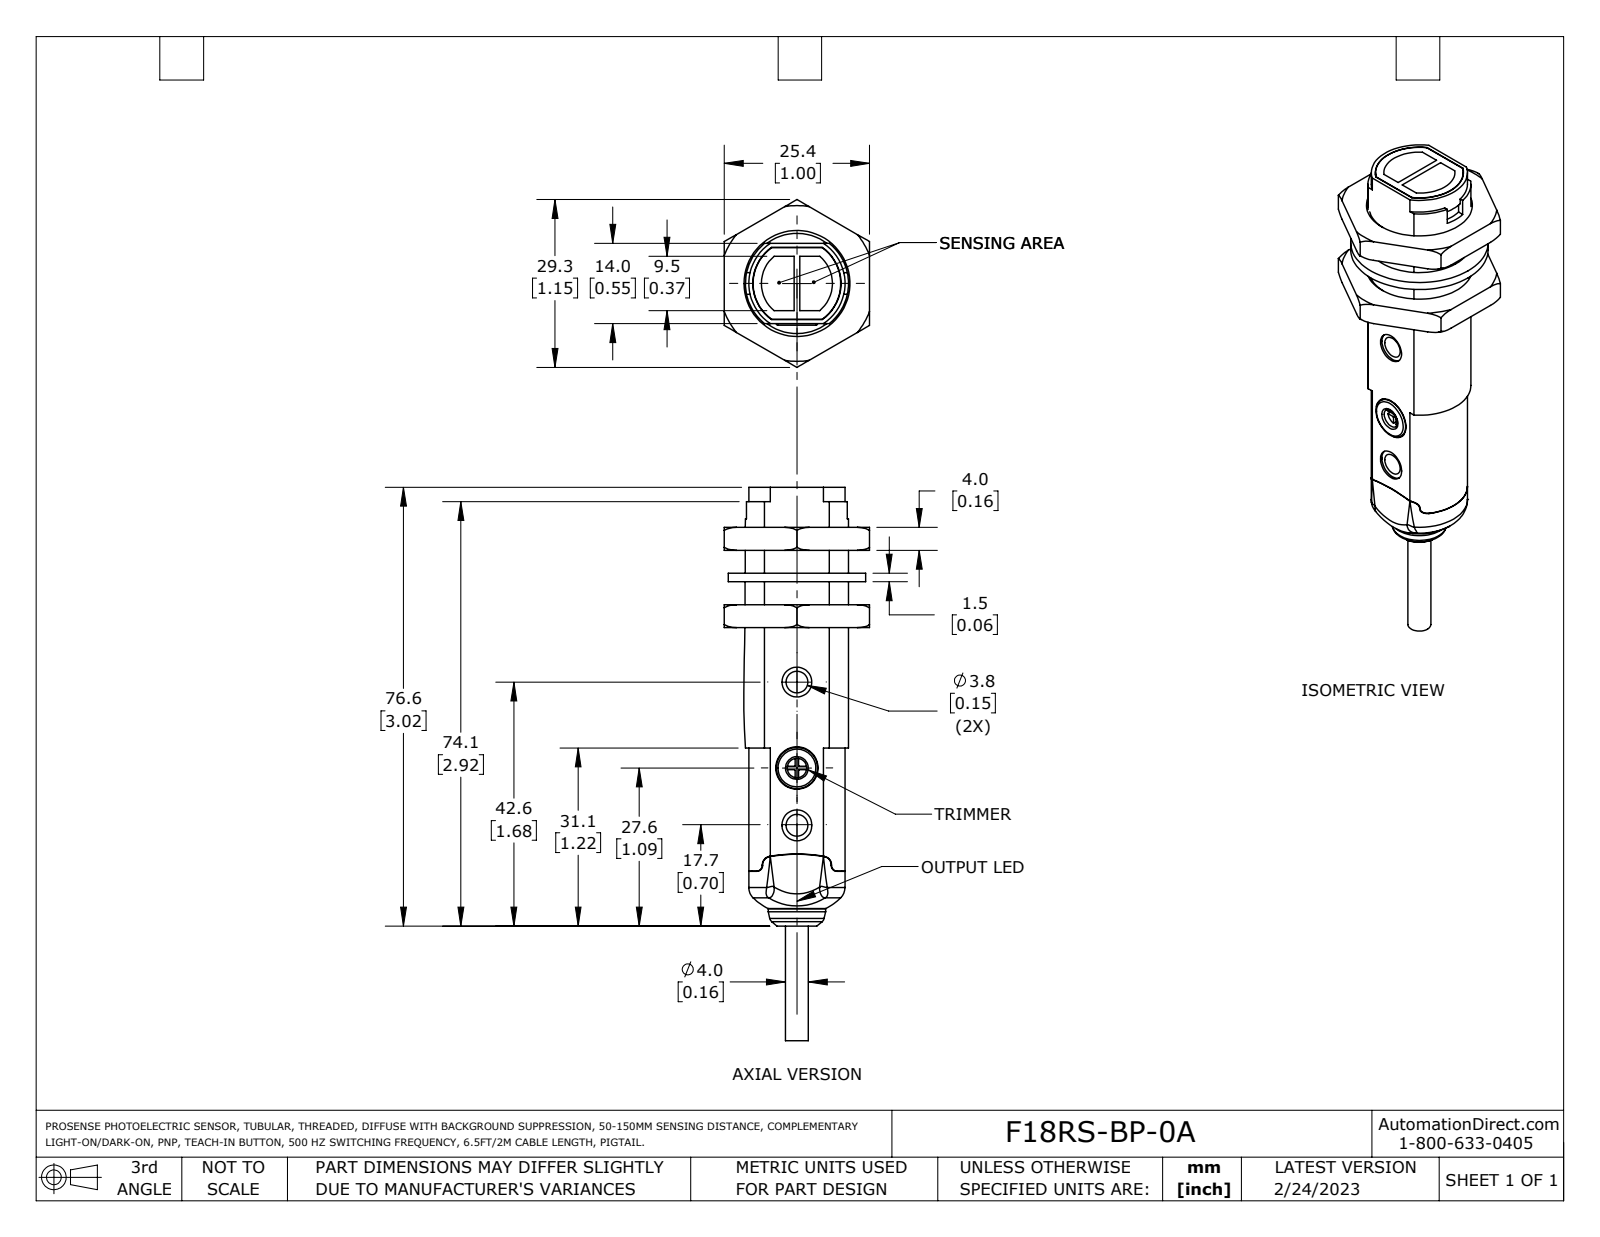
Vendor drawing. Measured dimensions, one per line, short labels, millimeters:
name: F18RS-BP-0A
written by: SolidWorks 2021 (AUTOMOTIVE_DESIGN)
unit: mm
bodies: 4 solids, 177 faces (80 planar, 47 cylindrical, 50 other)
size: 96.6 × 29.3 × 25.3
volume: 18 580 mm³; area: 8 097 mm²
holes: 2× ⌀3.8, 1× ⌀3.4, 1× ⌀5.2, 1× ⌀7.4, 1× ⌀17.5, 1× ⌀18
bosses: 1× ⌀24, 1× ⌀10, 1× ⌀7.2, 1× ⌀4
rounds: 4× R1, 4× R1.5, 2× R2.6, 2× R28, 1× R0.5, 1× R7.6, 1× R7.7, 1× R7.8
face distances: 4, 9.5, 14, 13.5, 5.5, 8, 25.3, 17.5, 11, 1.5
hole spacings: 10, 15, 25
